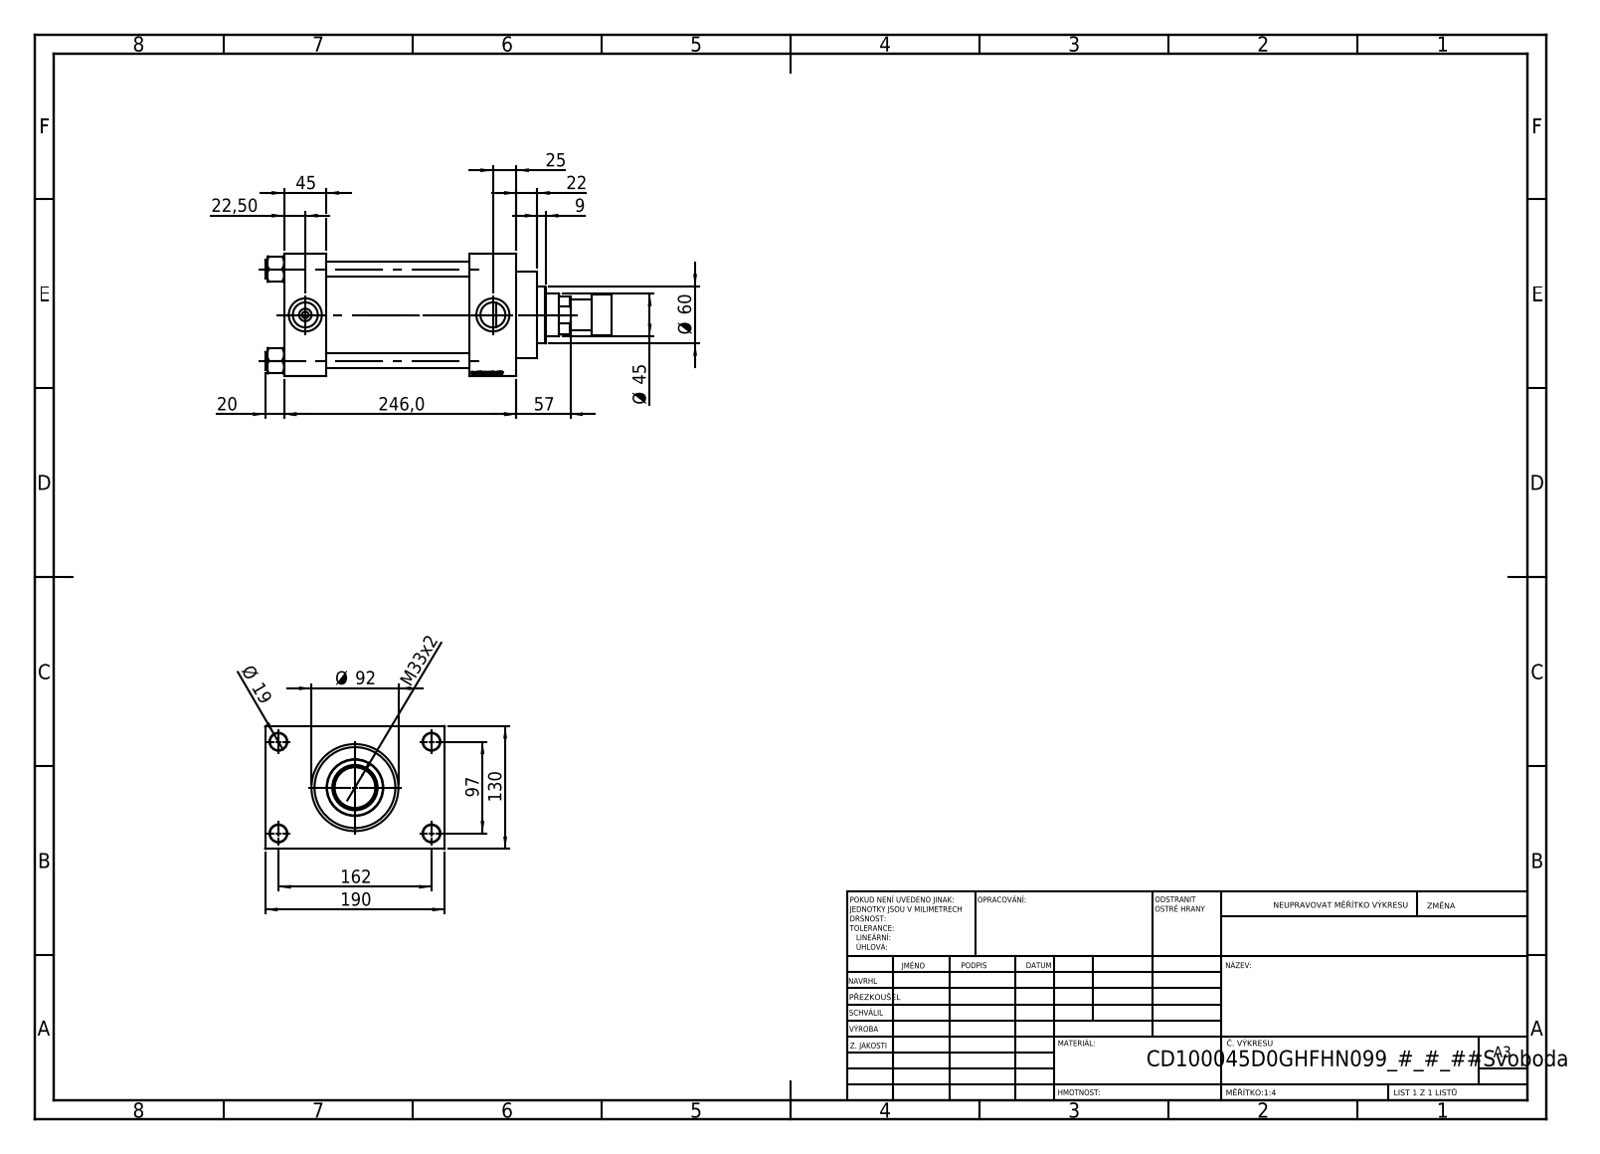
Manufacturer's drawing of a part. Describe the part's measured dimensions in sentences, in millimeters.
The part is named "V215CD_D_TYCINKA; V215CD_VC_A; V215CD_NUT_M5_D; V215CD_VCP_D (+2 more)". Its 3-D file was written by "SolidWorks 2019 (CONFIG_CONTROL_DESIGN)". It is 12 solids with 1164 faces: 548 planar, 92 cylindrical and 524 other. Overall it measures 367 by 190 by 130 millimeters. Its volume is 2 912 000 cubic millimeters and its surface area 442 424 square millimeters. Round holes: 4 of diameter 16, 4 of diameter 18, 2 of diameter 7, 2 of diameter 26.44, 2 of diameter 35, 1 of diameter 31.5, 1 of diameter 45, 1 of diameter 48, 1 of diameter 76, 1 of diameter 85.5, 1 of diameter 100. Round bosses or shafts: 4 of diameter 19, 1 of diameter 106, 1 of diameter 92, 1 of diameter 60, 1 of diameter 44, 1 of diameter 33. The main face-to-face distances are 130, 151, 45, 196, 246, 201, 50, 30, 160, 96. The hole center spacings are 32.55, 68.52, 94.41, 96.9, 102.27, 129.45, 161.73, 97.
